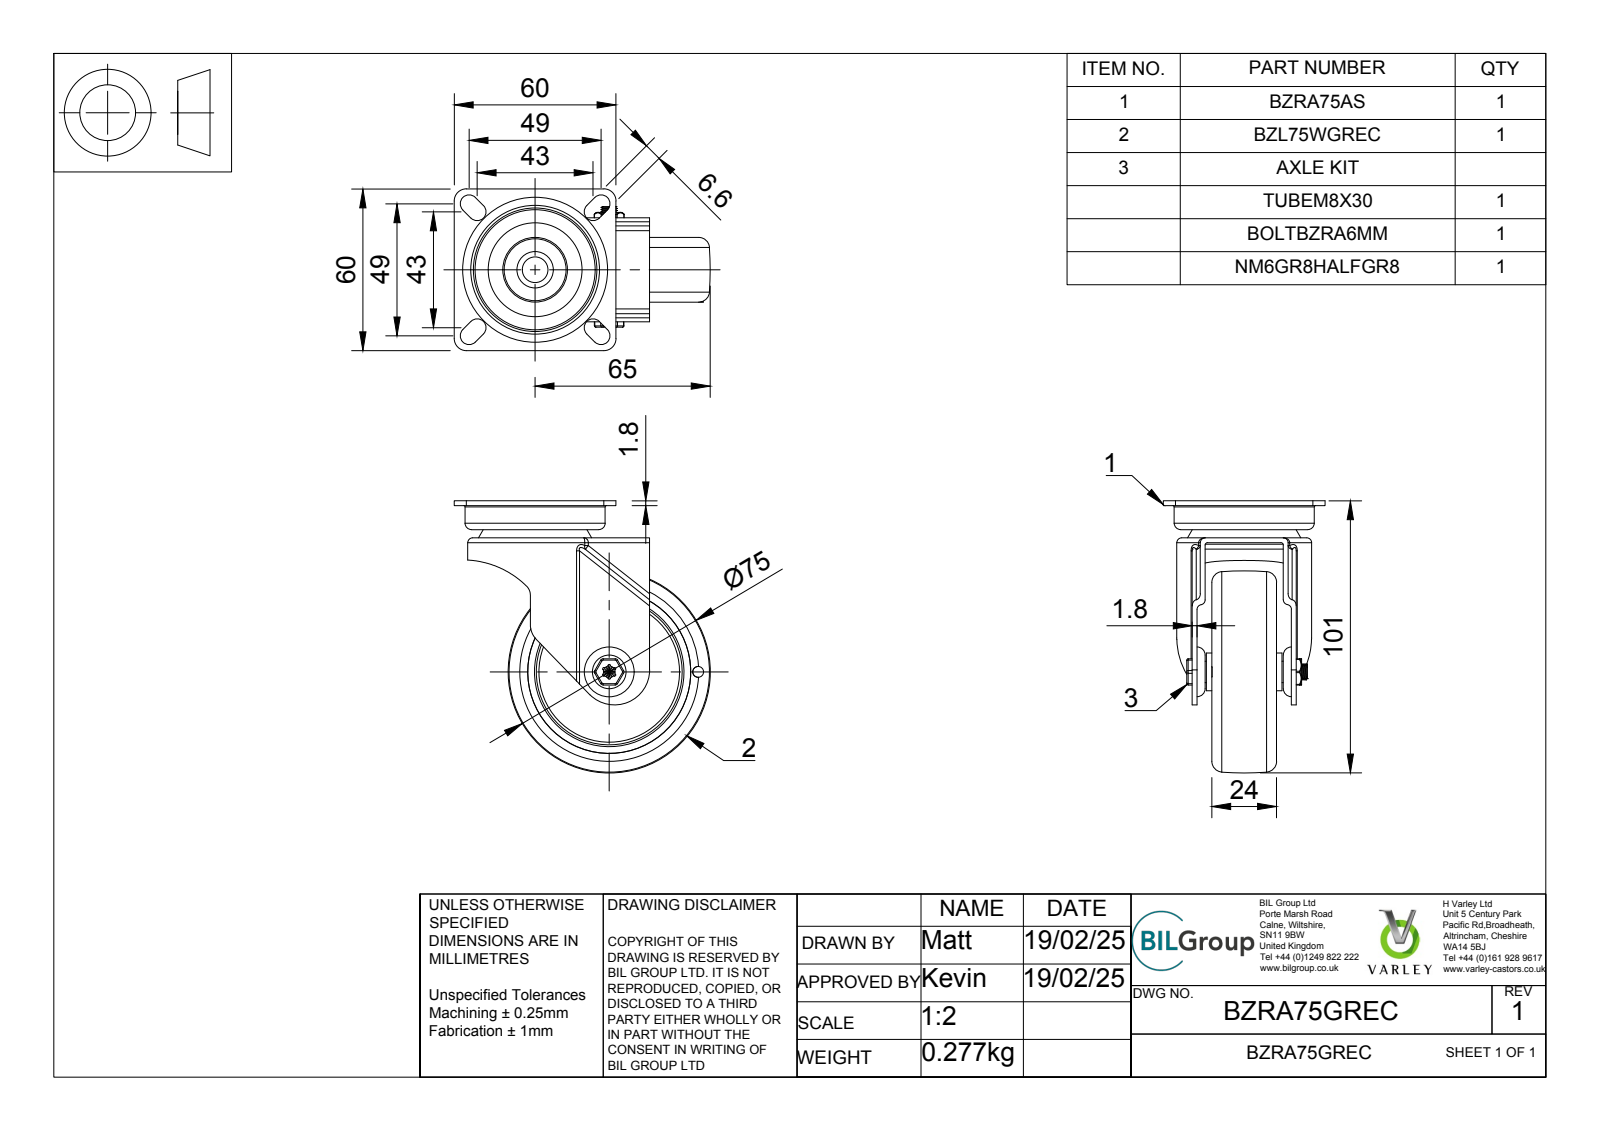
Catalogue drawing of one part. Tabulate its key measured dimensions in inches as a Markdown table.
| quantity | value |
| --- | --- |
| part name | BZRA50AS; ZINC PLATED PRESSED STEEL FORKS; ZINC PLATED PRESSED STEEL TOP PLATE; BZRA75GREC (+8 more) |
| STEP written by | Spatial InterOp 3D (AUTOMOTIVE_DESIGN) |
| units | inches |
| bodies | 8 solids, 452 faces (75 planar, 202 cylindrical, 175 other) |
| overall size | 3.077 × 2.913 × 2.362 |
| volume | 3.583 in³ |
| surface area | 71.9 in² |
| round holes (diameter × count) | 0.118 × 1, 0.236 × 1, 0.244 × 1, 0.248 × 1, 0.323 × 1, 0.374 × 1, 1.496 × 1, 1.652 × 1, 1.882 × 1 |
| round bosses / shafts (diameter × count) | 2.047 × 1, 1.535 × 1, 1.496 × 1, 0.591 × 1, 0.531 × 1, 0.315 × 1, 0.313 × 1, 0.197 × 1 |
| partial cylindrical surfaces (radius × count) | 0.039 × 18, 0.071 × 14, 0.02 × 12, 0.13 × 8, 0.016 × 6, 0.035 × 6, 0.177 × 4, 0.472 × 2 |
| main face-to-face distances | 0.071, 0.517, 0.394, 0.446, 0.587, 0.118, 1.358, 0.091, 0.551, 0.635 |
| hole center spacings | 0.748 |
